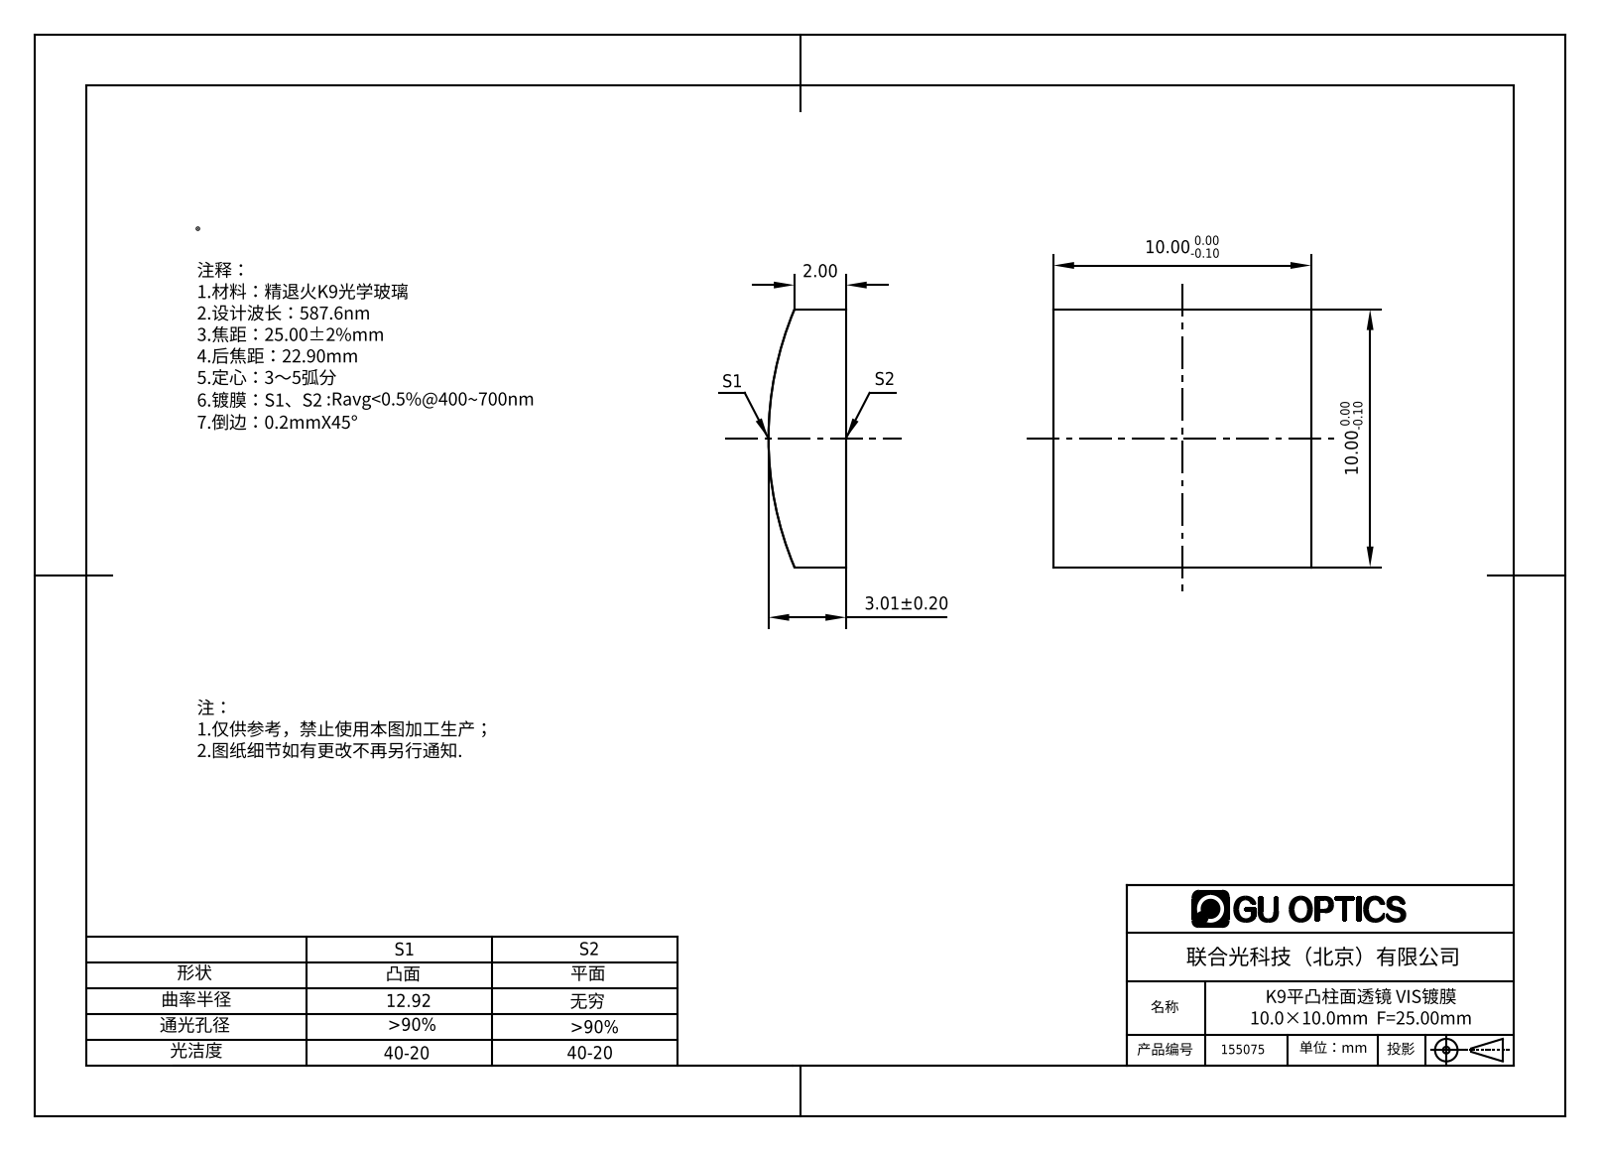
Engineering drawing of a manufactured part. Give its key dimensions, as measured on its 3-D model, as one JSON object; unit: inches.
{"part_name": "155009", "step_written_by": "SolidWorks 2016 (AUTOMOTIVE_DESIGN)", "units": "inches", "bodies": {"solids": 1, "faces": 6, "planar": 5, "cylindrical": 1, "other": 0}, "overall_size": [0.394, 0.394, 0.119], "volume_in3": 0.016, "surface_area_in2": 0.459, "partial_cylinders_radius": [[0.509, 1]], "face_to_face_distances": [0.394]}
